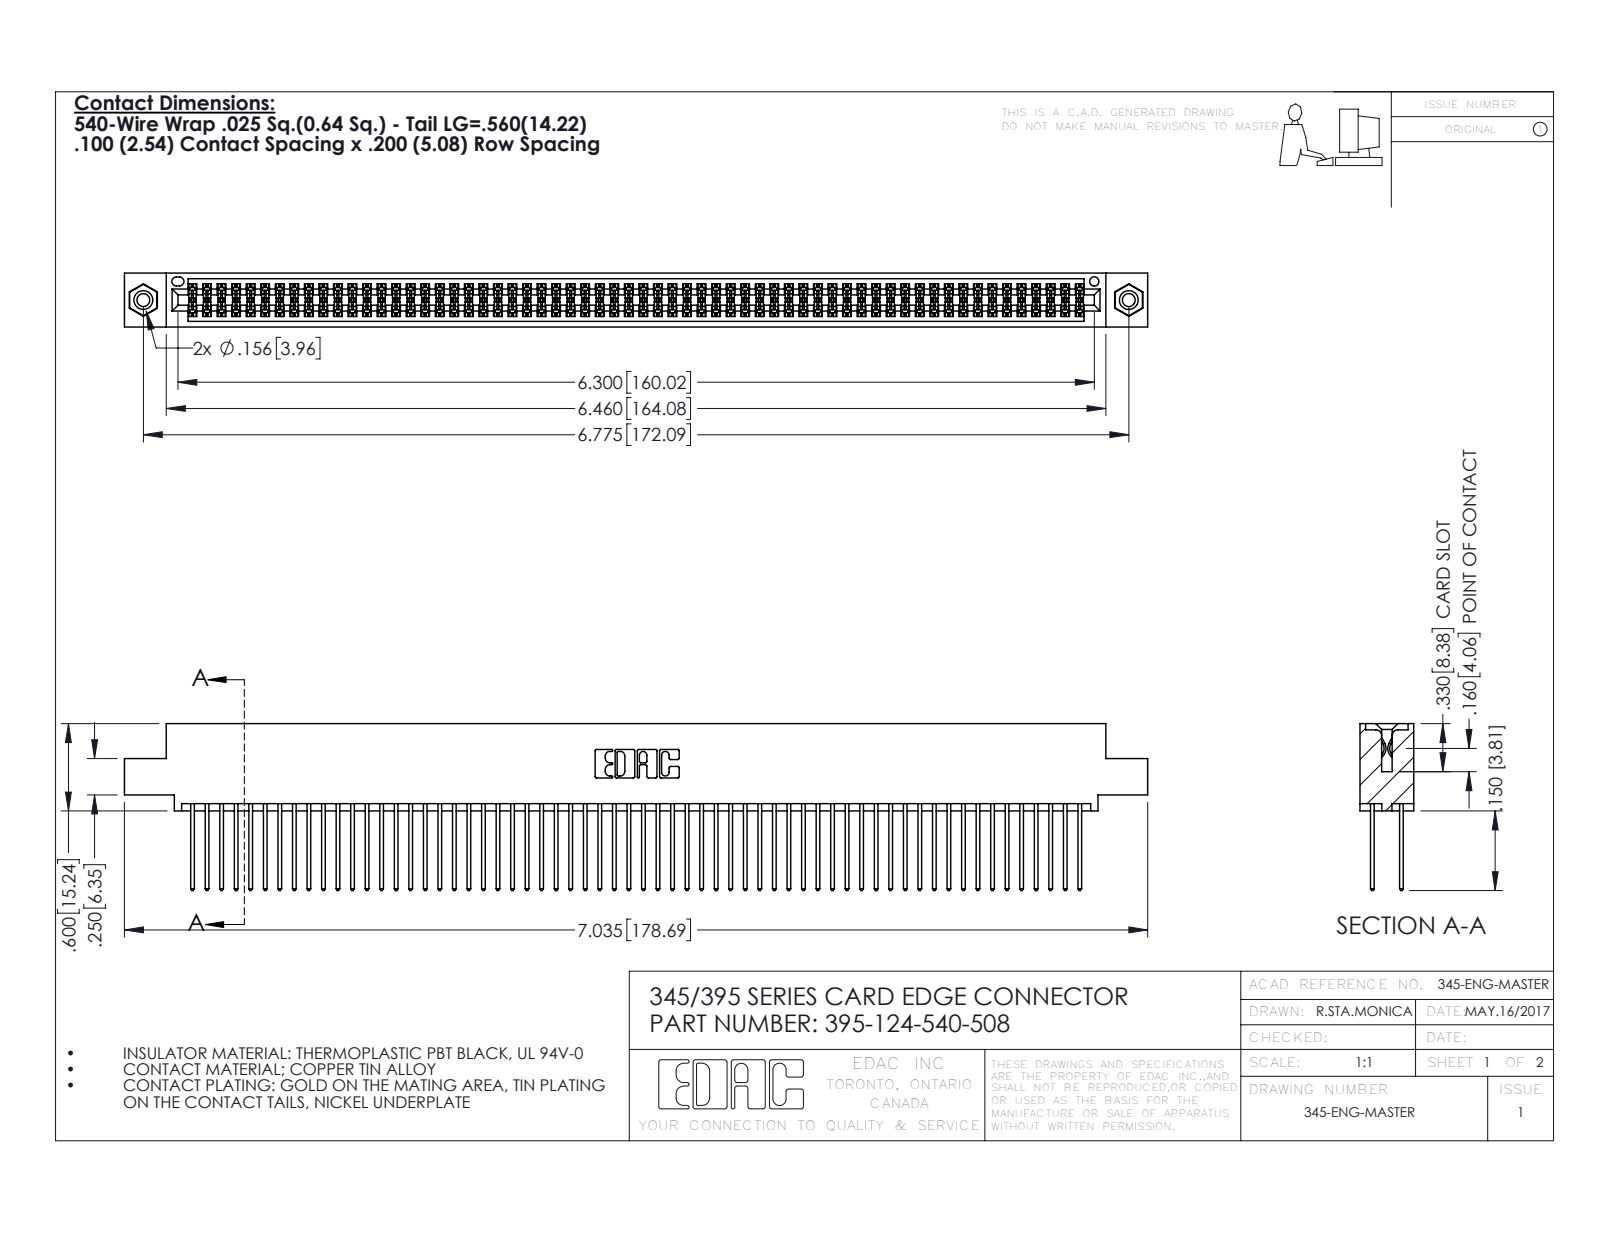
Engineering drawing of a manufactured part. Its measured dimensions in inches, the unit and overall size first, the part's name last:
Units: inches
Overall size (bounding box): 7.035 × 1.147 × 0.37
Round holes (diameter × count): ⌀0.089 ×2, ⌀0.125 ×2, ⌀0.156 ×2, ⌀0.064 ×1
Round bosses / shafts (diameter × count): ⌀0.155 ×2
Partial cylindrical surfaces — rounded edges, fillets, slot ends (radius × count): R0.006 ×186, R0.01 ×124, R0.01 ×22, R0.007 ×6, R0.031 ×6, R0.026 ×3, R0.014 ×2, R0.019 ×2
Main face-to-face distances: 0.072, 0.298, 0.2, 0.098, 0.272, 0.025, 0.225, 0.37, 0.175, 0.149
Hole centre spacings: 0.27, 6.539, 6.775
Volume: 1.094 in³ · Surface area: 45.23 in²
Bodies: 127 solids, 6390 faces (4208 planar, 2166 cylindrical, 16 other)
Part name (STEP PRODUCT): 395-124-540-508; 345 Part_0.110 Offset - 0.156 Dia-TI; 345-250-001_345-250-003-102; 345-292-001_345-293-140
STEP written by: SolidWorks 2016 (CONFIG_CONTROL_DESIGN)
